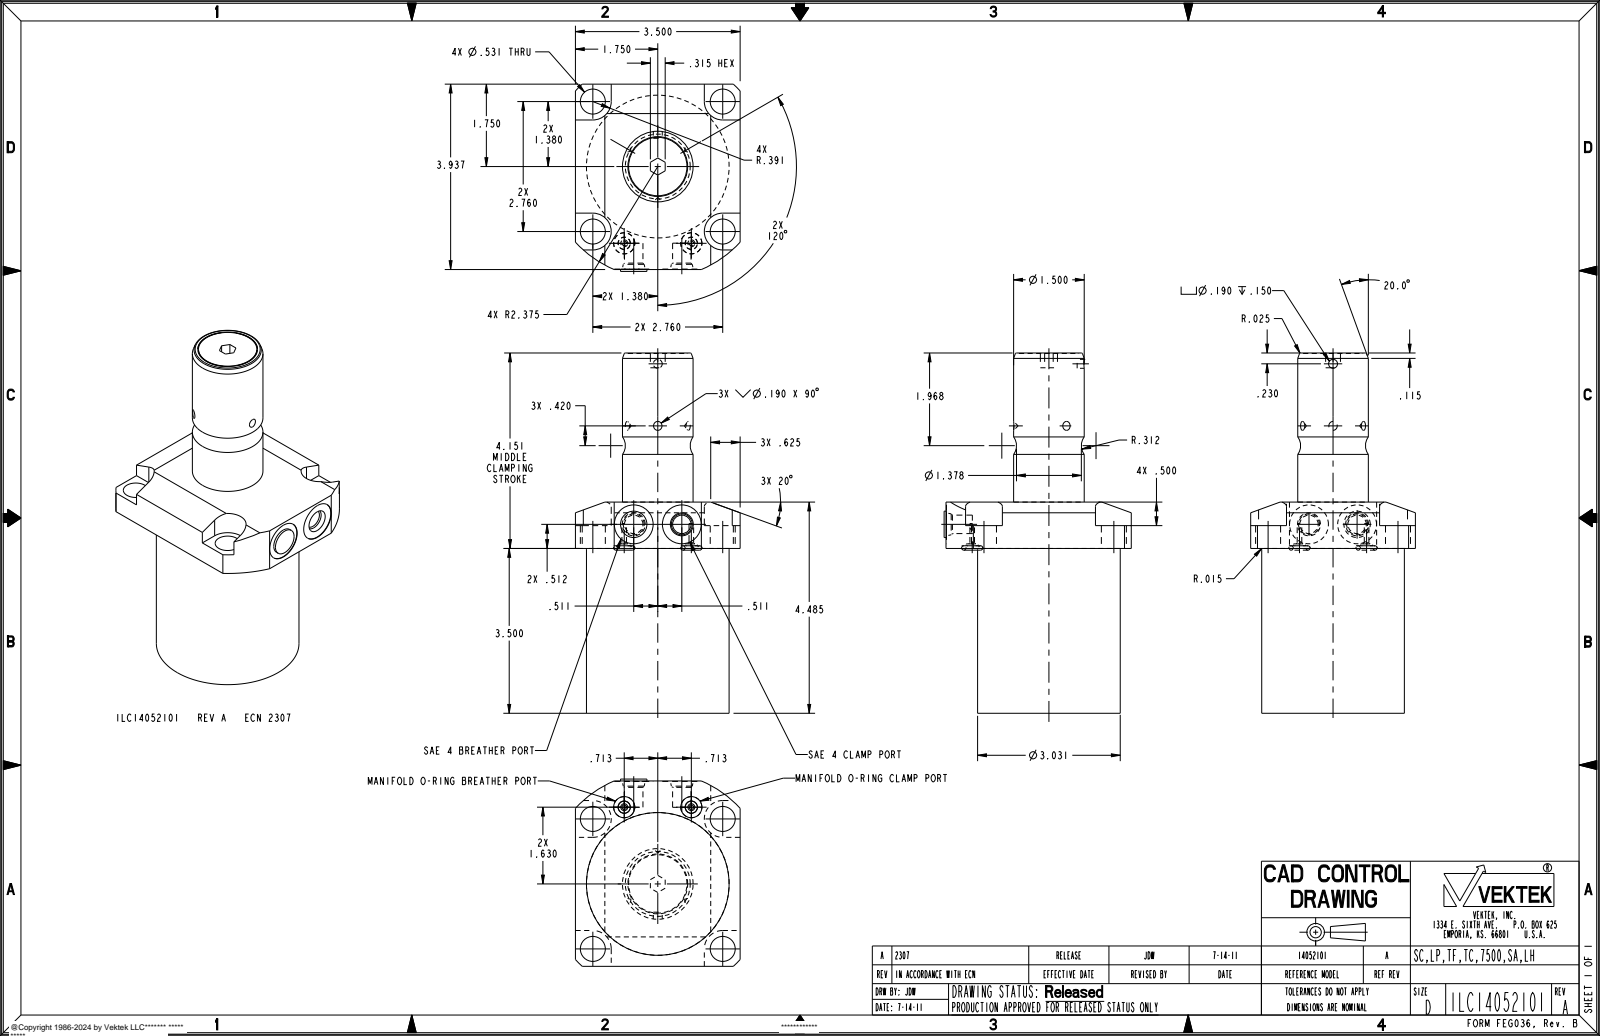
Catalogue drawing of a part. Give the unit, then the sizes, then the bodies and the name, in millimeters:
Units: millimetres
Overall size (bounding box): 194.3 × 101 × 88.9
Round holes (diameter × count): ⌀13.5 ×4, ⌀2.5 ×2, ⌀6.5 ×2, ⌀10 ×2, ⌀11.4 ×2, ⌀21 ×2, ⌀4.8 ×1, ⌀32.3 ×1
Round bosses / shafts (diameter × count): ⌀77 ×1, ⌀38.1 ×1, ⌀31.5 ×1, ⌀14.2 ×1
Partial cylindrical surfaces — rounded edges, fillets, slot ends (radius × count): R9.9 ×4, R60.3 ×1
Main face-to-face distances: 88.9, 113.9, 25, 80.4, 194.3, 105.4, 101.2, 12.3, 12.7, 93.1
Hole centre spacings: 49.6, 70.1, 18.1, 45.2, 53.5, 78.3, 87.1, 93.1
Volume: 685 300 mm³ · Surface area: 59 700 mm²
Bodies: 3 solids, 131 faces (47 planar, 50 cylindrical, 34 other)
Part name (STEP PRODUCT): ILC14052101
STEP written by: PRO/ENGINEER BY PARAMETRIC TECHNOLOGY CORPORATION, 2007460 (AUTOMOTIVE_DESIGN_CC2)
